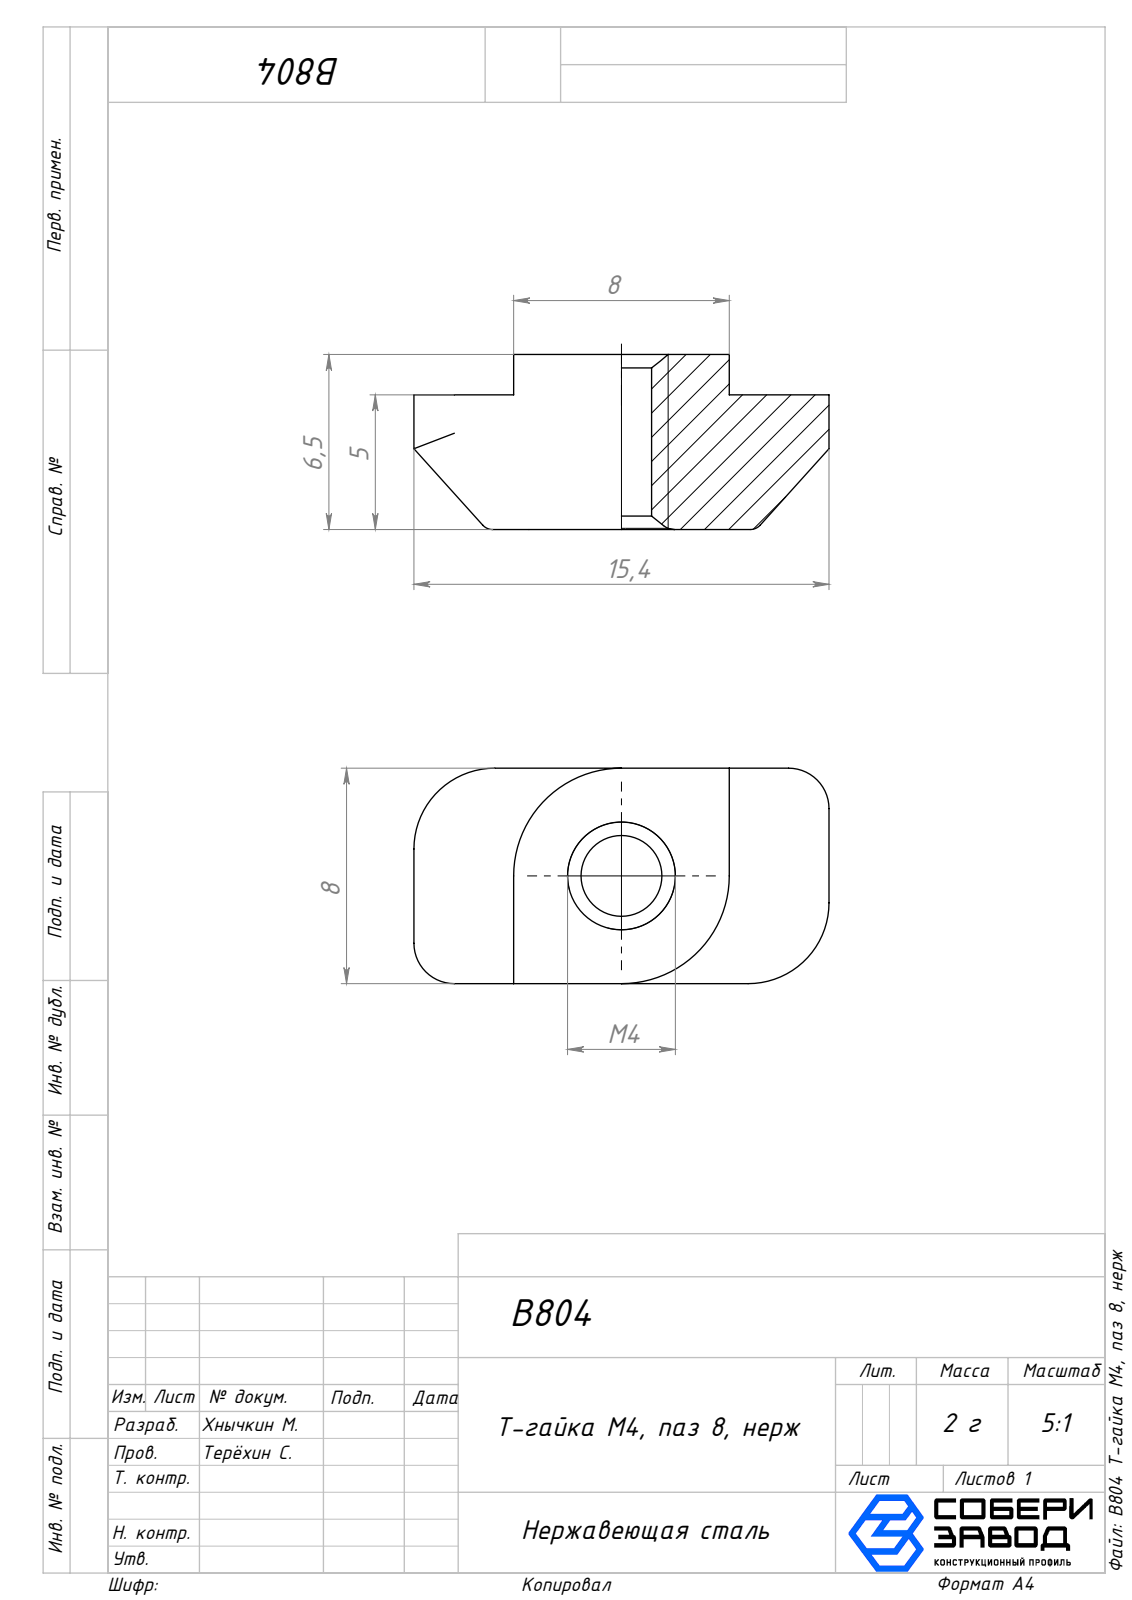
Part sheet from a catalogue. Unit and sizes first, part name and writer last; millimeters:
Units: millimetres
Overall size (bounding box): 15.4 × 8 × 6.5
Round holes (diameter × count): ⌀3 ×1
Partial cylindrical surfaces — rounded edges, fillets, slot ends (radius × count): R0.5 ×4, R1.5 ×4, R3 ×4, R4 ×1
Main face-to-face distances: 8, 5, 6.5, 1.5, 3.7, 11.7, 15.4
Volume: 558 mm³ · Surface area: 485 mm²
Bodies: 1 solid, 38 faces (12 planar, 16 cylindrical, 10 other)
Part name (STEP PRODUCT): B804 Т-гайка М4, паз 8, нерж
STEP written by: SolidWorks 2025 (AUTOMOTIVE_DESIGN)
